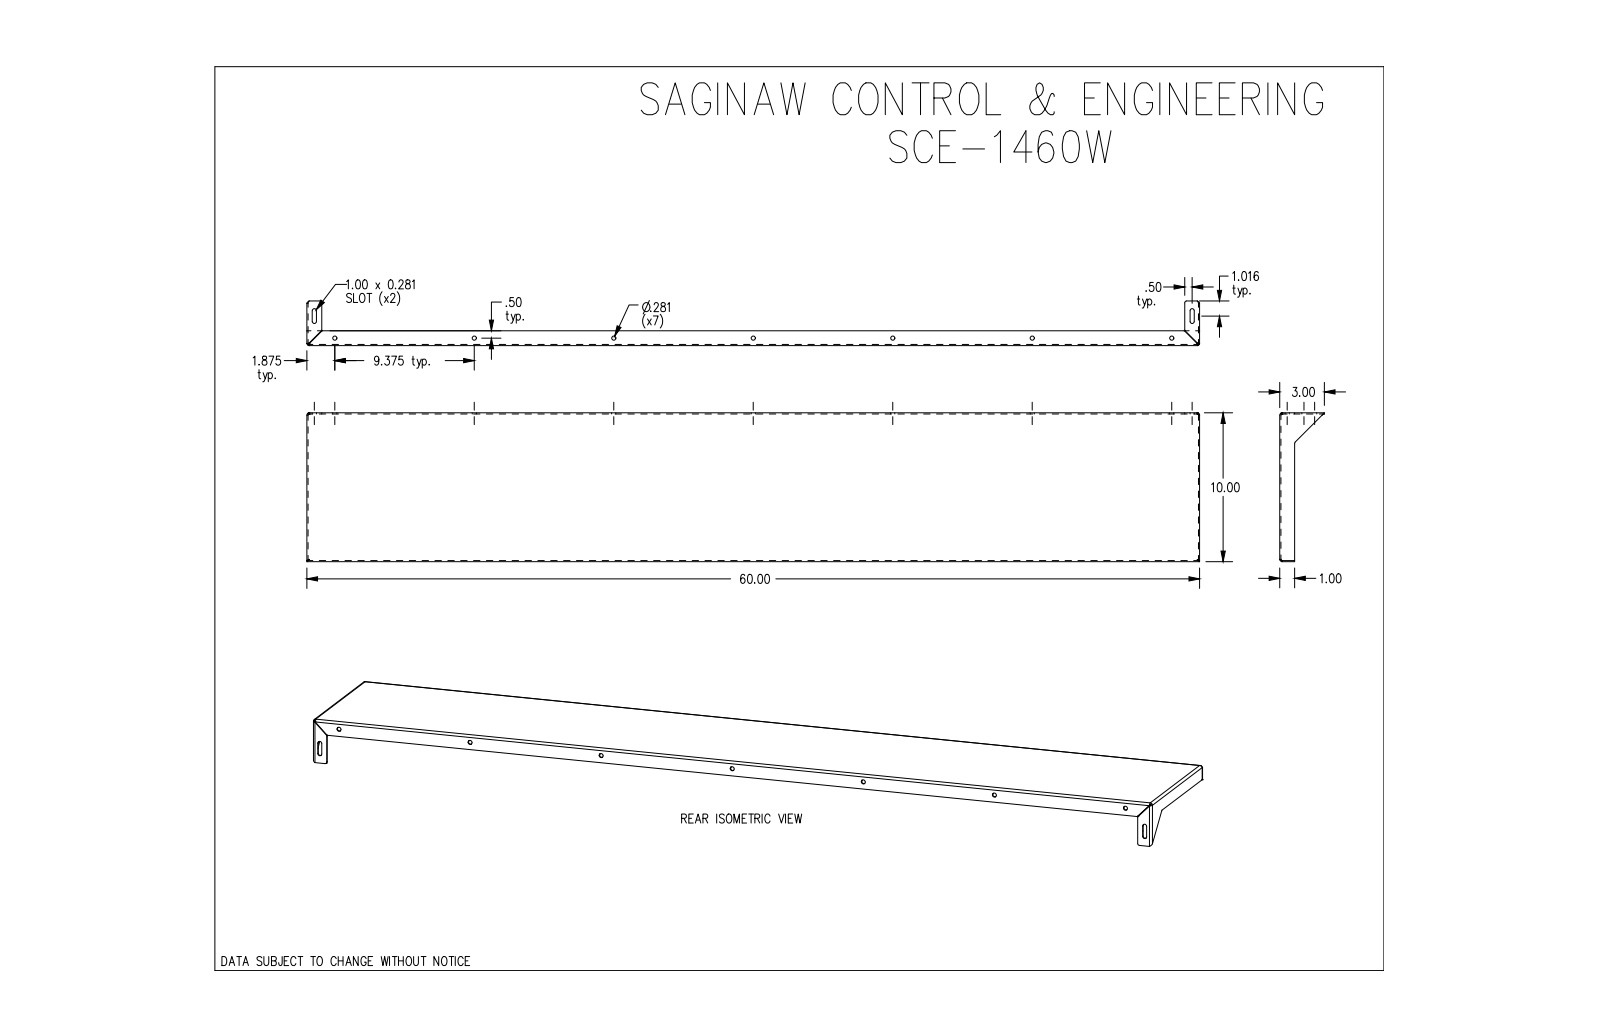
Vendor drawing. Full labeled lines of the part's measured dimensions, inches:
Part name (STEP PRODUCT): SCE-1460W
STEP written by: SolidWorks 2019 (AUTOMOTIVE_DESIGN)
Units: inches
Bodies: 1 solid, 47 faces (28 planar, 17 cylindrical, 2 other)
Overall size (bounding box): 60 × 10 × 3
Volume: 36.69 in³ · Surface area: 1 475 in²
Round holes (diameter × count): ⌀0.281 ×7
Partial cylindrical surfaces — rounded edges, fillets, slot ends (radius × count): R0.141 ×4, R0.106 ×2, R0.156 ×2, R0.125 ×1
Main face-to-face distances: 0.05, 9.95, 10, 9.9, 59.95, 60, 59.9, 0.95, 1, 9.94
Hole centre spacings: 9.375, 18.75, 28.126, 37.501, 46.876, 56.251
